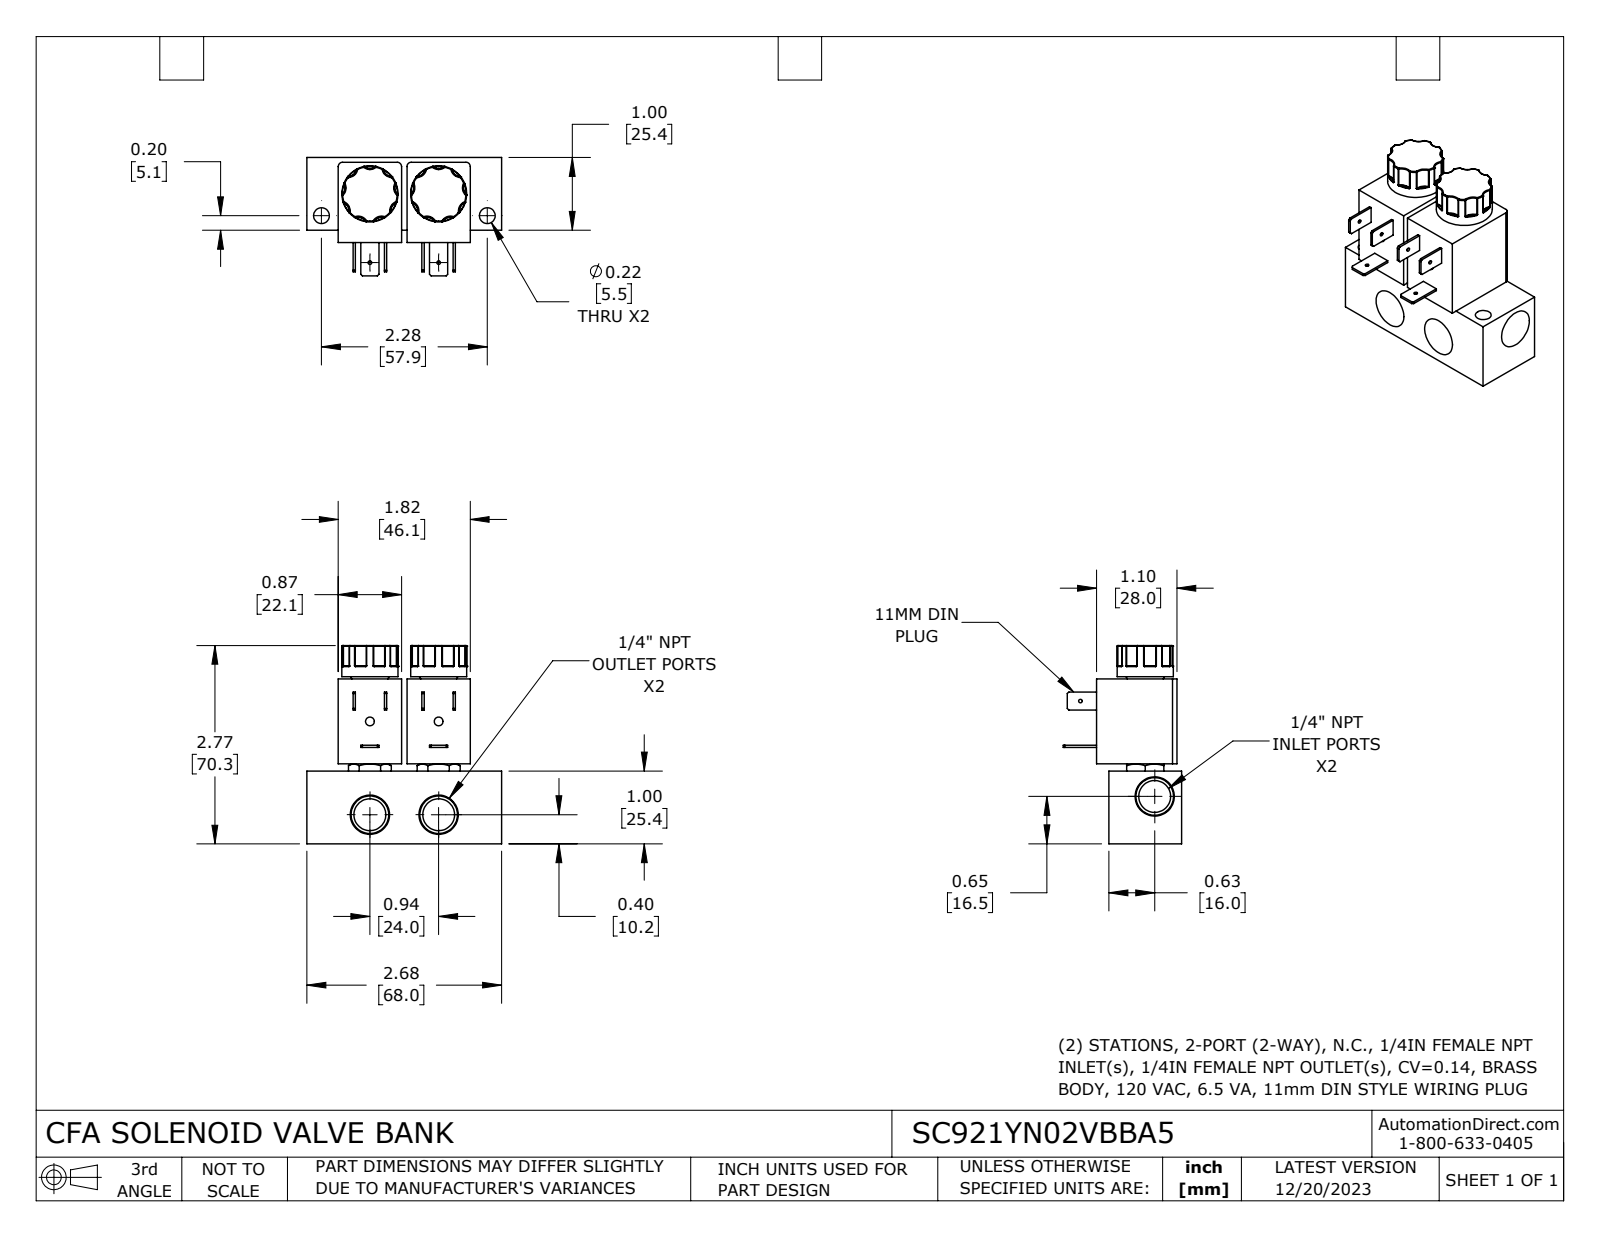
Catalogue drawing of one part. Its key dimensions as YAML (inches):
part_name: "SC921YN02VBBA5"
step_written_by: "SolidWorks 2023 (CONFIG_CONTROL_DESIGN)"
units: inches
bodies: {solids: 1, faces: 446, planar: 100, cylindrical: 96, other: 250}
overall_size: [2.725, 2.677, 1.627]
volume: 4.833
surface_area: 34.57
round_holes:
  - {diameter: 0.05, count: 3}
  - {diameter: 0.438, count: 3}
  - {diameter: 0.12, count: 2}
  - {diameter: 0.217, count: 2}
round_bosses_or_shafts:
  - {diameter: 0.77, count: 2}
partial_cylinders:
  - {radius: 0.01, count: 36}
  - {radius: 0.133, count: 18}
  - {radius: 0.06, count: 4}
face_to_face_distances: [1, 0.945, 0.87, 1.169, 0.169, 0.065, 0.935, 1.104, 0.431, 1.301]
hole_center_spacings: [0.945, 1.282, 1.593, 0.928, 0.93, 1.662, 1.735, 1.738]
